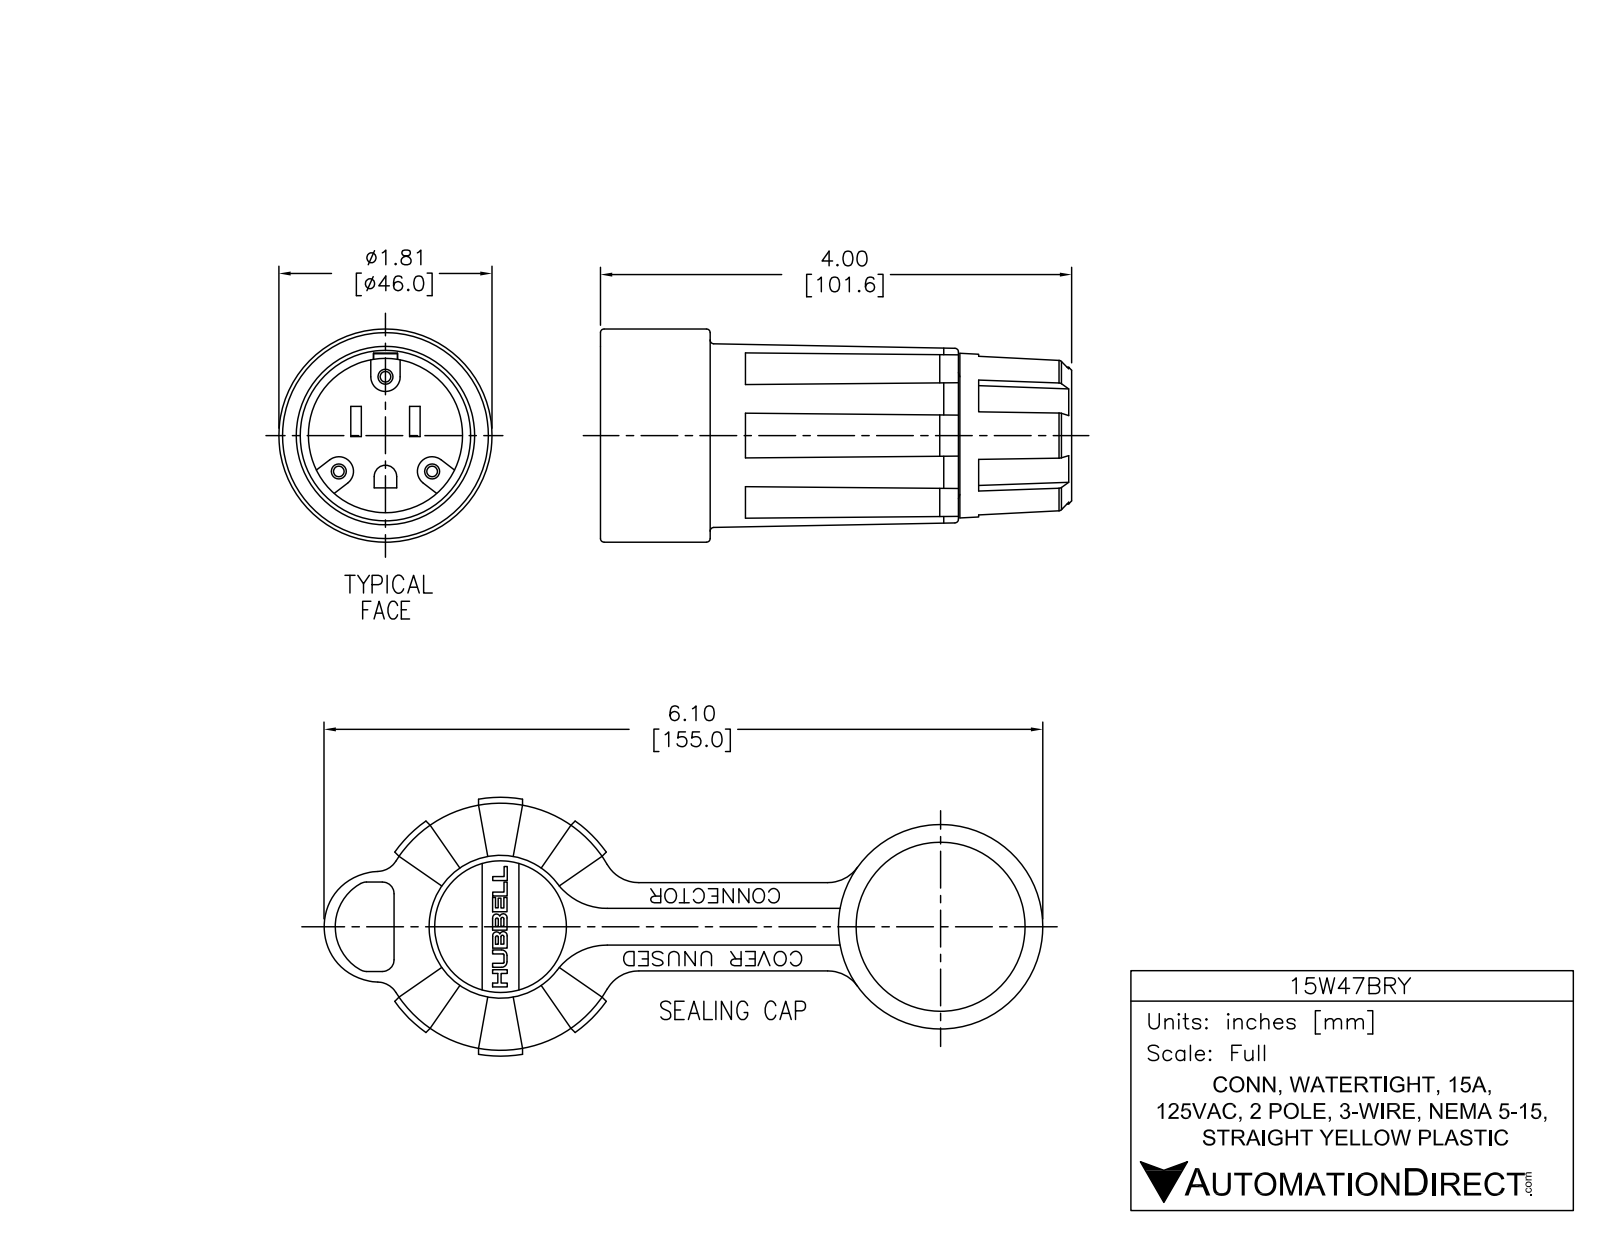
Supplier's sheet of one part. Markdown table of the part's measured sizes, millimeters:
| quantity | value |
| --- | --- |
| part name | 15W47BRY |
| STEP written by | SolidWorks 2013 (AUTOMOTIVE_DESIGN) |
| units | millimeters |
| bodies | 1 solid, 381 faces (181 planar, 89 cylindrical, 111 other) |
| overall size | 157.5 × 104.3 × 55.9 |
| volume | 122 800 mm³ |
| surface area | 38 490 mm² |
| round holes (diameter × count) | 15.9 × 1, 29.2 × 1, 30.5 × 1, 38.1 × 1, 47 × 1 |
| round bosses / shafts (diameter × count) | 5.1 × 3, 47.5 × 1, 46.4 × 1, 39.6 × 1, 37.8 × 1, 33.8 × 1, 25.4 × 1 |
| partial cylindrical surfaces (radius × count) | 0.4 × 16, 6.4 × 4, 1.4 × 3, 2.8 × 3, 2.5 × 2, 3 × 2, 2.7 × 1, 9.5 × 1 |
| main face-to-face distances | 3.6, 1.5, 11.4, 2, 1.3, 7.6, 55.9, 52.3, 53.8, 4.2 |
| hole center spacings | 96.5 |
